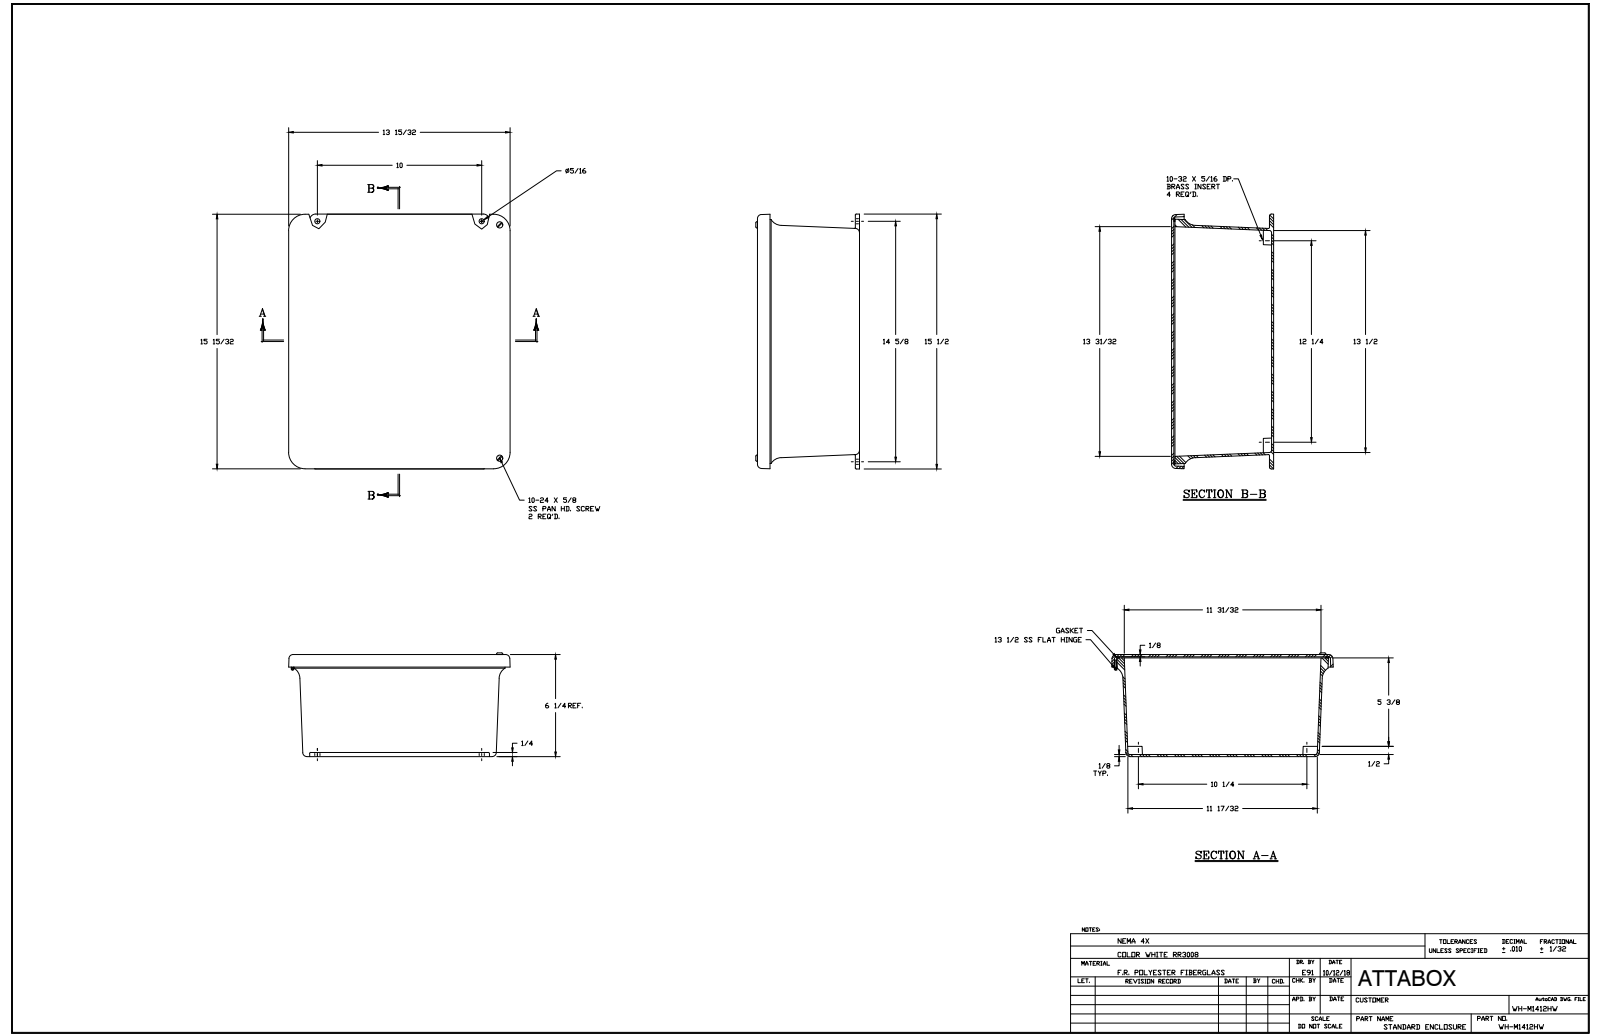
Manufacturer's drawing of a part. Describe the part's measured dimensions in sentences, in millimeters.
The part is named "WH-M1412HW". Its 3-D file was written by "SolidWorks 2018 (AUTOMOTIVE_DESIGN)". It is 24 solids with 858 faces: 317 planar, 334 cylindrical and 207 other. Overall it measures 393.7 by 343 by 161.1 millimeters. Its volume is 1 852 000 cubic millimeters and its surface area 1 014 000 square millimeters. Round holes: 10 of diameter 3.3, 10 of diameter 3.6, 8 of diameter 3.9, 4 of diameter 4, 4 of diameter 5.5, 2 of diameter 3.7, 1 of diameter 2.2, 1 of diameter 2.2. Round bosses or shafts: 10 of diameter 6.4, 6 of diameter 6.9, 5 of diameter 3.2, 5 of diameter 3.2, 2 of diameter 4.8, 2 of diameter 4, 1 of diameter 3.9, 1 of diameter 3.9. Partial cylindrical surfaces (rounded edges, fillets, slot ends): 20 of radius 0.8, 12 of radius 3.2, 12 of radius 6.4, 4 of radius 5.1, 4 of radius 9.5, 4 of radius 19.1, 2 of radius 1.6. The main face-to-face distances are 3.2, 3.4, 154.4, 157.8, 151.2, 154.6, 3.2, 8.4, 3.9, 2. The hole center spacings are 82.6, 165.1, 247.7, 6.4, 76.2, 34.8, 158.8, 286.
